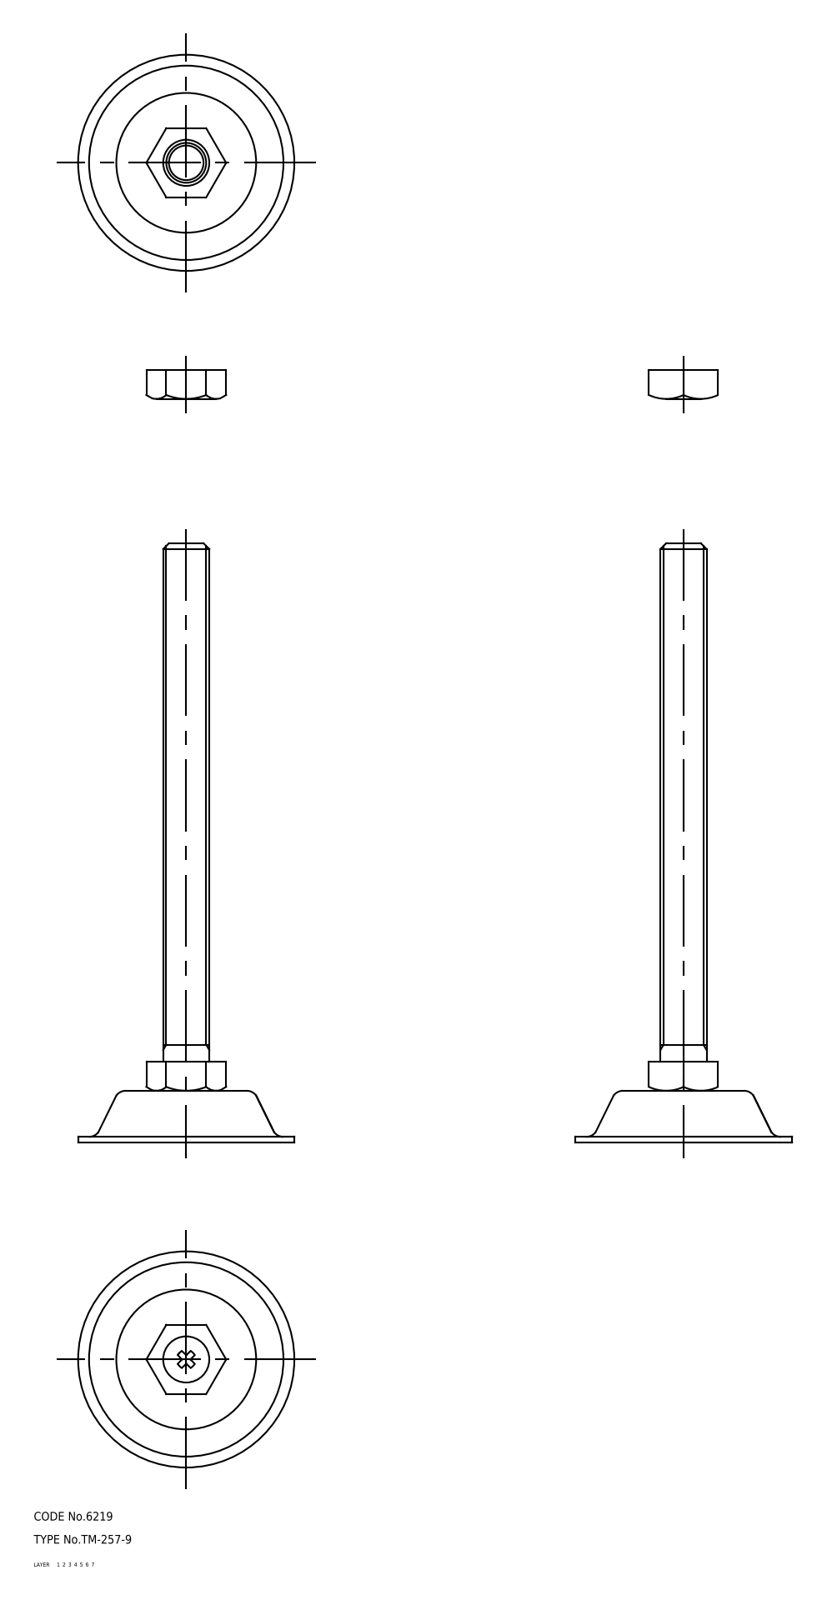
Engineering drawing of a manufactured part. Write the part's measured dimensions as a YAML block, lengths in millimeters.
part_name: "nut; foot; bolt; TM_257_9_10054_36"
step_written_by: "CADfix (AUTOMOTIVE_DESIGN)"
units: millimeters
bodies: {solids: 4, faces: 83, planar: 0, cylindrical: 0, other: 83}
overall_size: [208, 75, 75]
volume: 61078
surface_area: 27330
